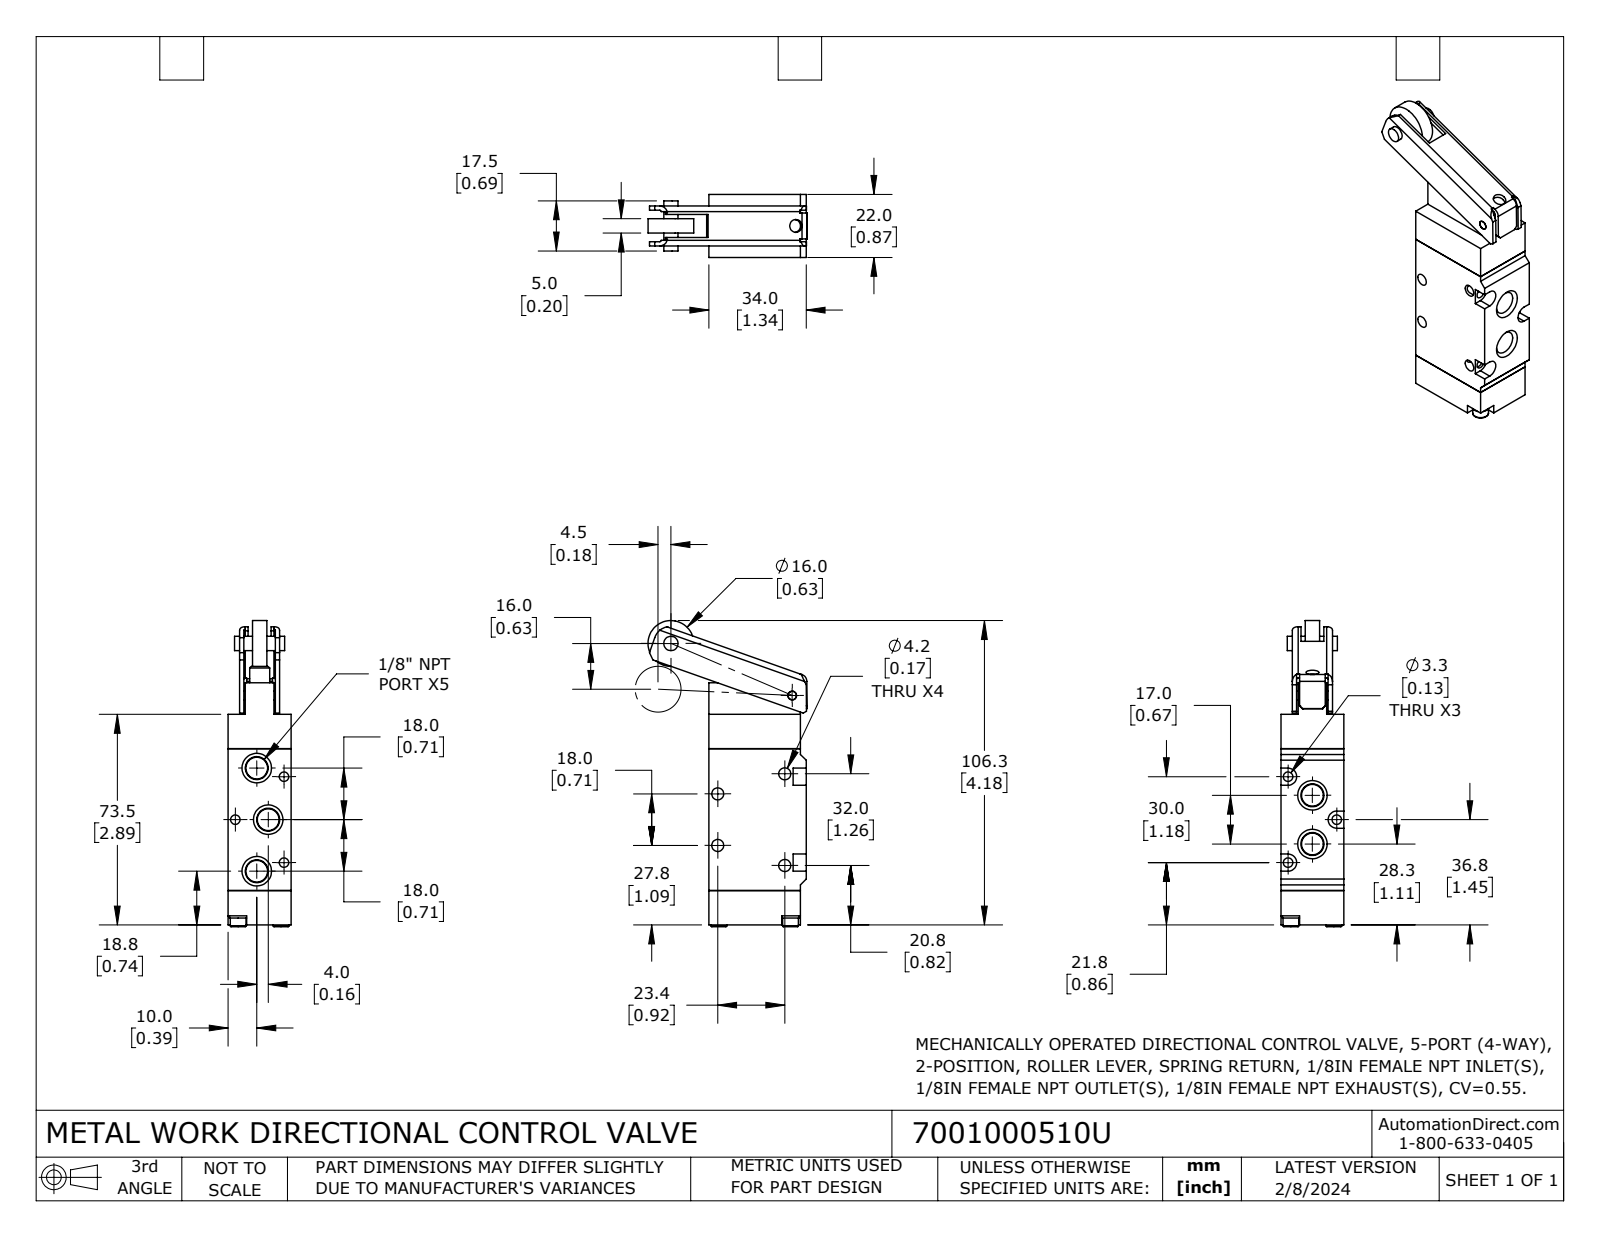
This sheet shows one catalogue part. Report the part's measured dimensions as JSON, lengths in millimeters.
{"part_name": "7001000510U", "step_written_by": "SolidWorks 2023 (CONFIG_CONTROL_DESIGN)", "units": "millimeters", "bodies": {"solids": 9, "faces": 240, "planar": 121, "cylindrical": 69, "other": 50}, "overall_size": [106.9, 55.5, 22], "volume_mm3": 57170, "surface_area_mm2": 21730, "round_holes": [[4.2, 4], [3, 3], [3.3, 3], [4.5, 1], [5, 1]], "round_bosses_or_shafts": [[6, 2], [5.5, 2], [16, 1], [7, 1]], "partial_cylinders_radius": [[3, 3], [0.5, 2], [2, 2], [1, 1], [2.5, 1], [6, 1]], "face_to_face_distances": [22, 12, 1.5, 2, 49.5, 4, 18, 5.5, 16.5, 12.5], "hole_center_spacings": [22.7, 24.4, 34.2, 18, 27.5, 29.2, 30, 32]}
